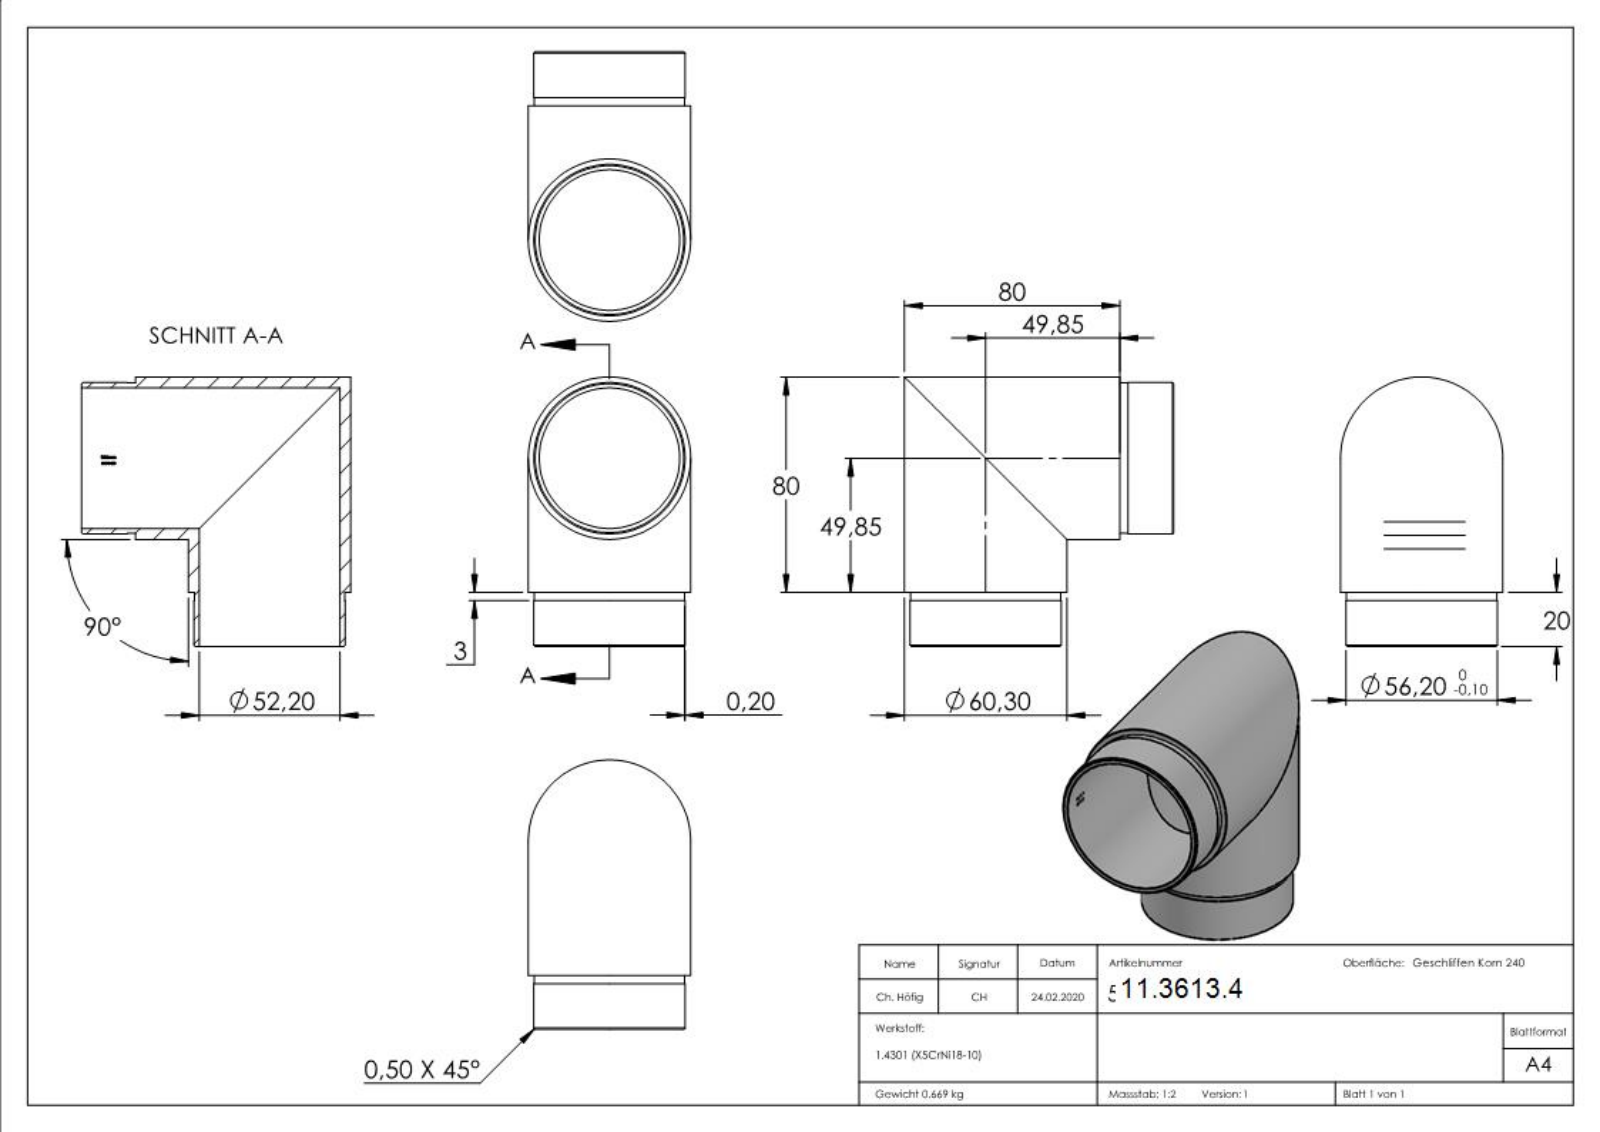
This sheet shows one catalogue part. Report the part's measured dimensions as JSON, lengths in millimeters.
{"part_name": "56173-320", "step_written_by": "SolidWorks 2015 (CONFIG_CONTROL_DESIGN)", "units": "millimeters", "bodies": {"solids": 1, "faces": 237, "planar": 97, "cylindrical": 30, "other": 110}, "overall_size": [100, 100, 60.3], "volume_mm3": 84721, "surface_area_mm2": 50325, "round_holes": [[52.2, 2]], "round_bosses_or_shafts": [[60.3, 2], [56.2, 2], [55.8, 2]], "partial_cylinders_radius": [[26.2, 1]], "face_to_face_distances": [20, 17, 3, 1.78, 0.83, 0.76, 0.79, 0.99, 2.45, 2.77]}
